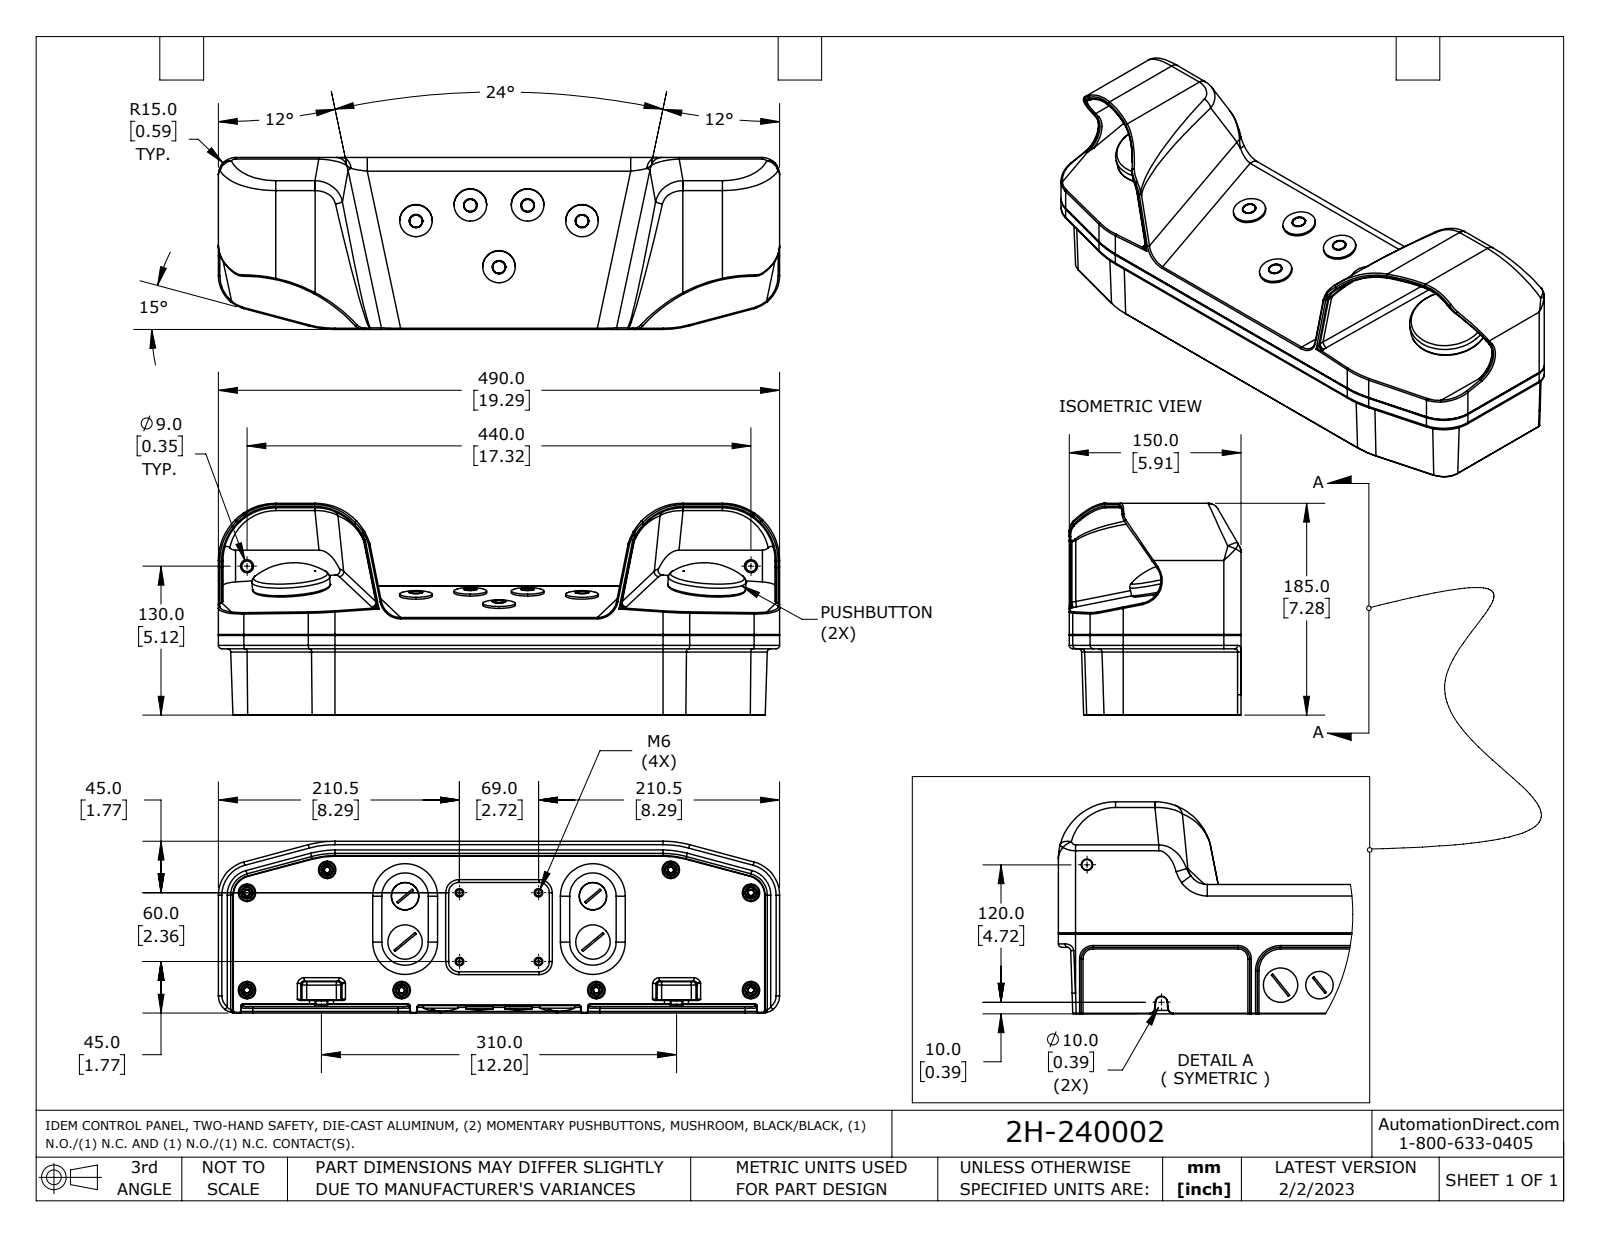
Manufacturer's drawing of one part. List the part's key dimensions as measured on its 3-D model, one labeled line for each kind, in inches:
Part name (STEP PRODUCT): 2H-240002
STEP written by: SolidWorks 2021 (AUTOMOTIVE_DESIGN)
Units: inches
Bodies: 1 solid, 1400 faces (393 planar, 445 cylindrical, 562 other)
Overall size (bounding box): 19.291 × 7.283 × 5.906
Volume: 421.4 in³ · Surface area: 678.5 in²
Round holes (diameter × count): ⌀0.528 ×8, ⌀0.433 ×5, ⌀0.626 ×5, ⌀0.886 ×5, ⌀0.197 ×4, ⌀0.217 ×4, ⌀0.571 ×4, ⌀0.205 ×2, ⌀0.354 ×2, ⌀0.701 ×2, ⌀0.78 ×2, ⌀0.969 ×2
Round bosses / shafts (diameter × count): ⌀0.394 ×8, ⌀1.118 ×5, ⌀0.878 ×5, ⌀0.465 ×5, ⌀1.181 ×4, ⌀0.945 ×4, ⌀0.906 ×4, ⌀0.709 ×4
Partial cylindrical surfaces — rounded edges, fillets, slot ends (radius × count): R0.02 ×129, R0.059 ×35, R0.118 ×22, R0.047 ×15, R0.394 ×10, R0.197 ×9, R0.157 ×8, R0.787 ×7
Main face-to-face distances: 0.157, 0.098, 5.906, 0.256, 7.126, 5.65, 7.028, 7.283, 7.185, 0.315
Hole centre spacings: 1.95, 3.878, 5.709, 3.279, 1.969, 2.378, 3.279, 17.323
